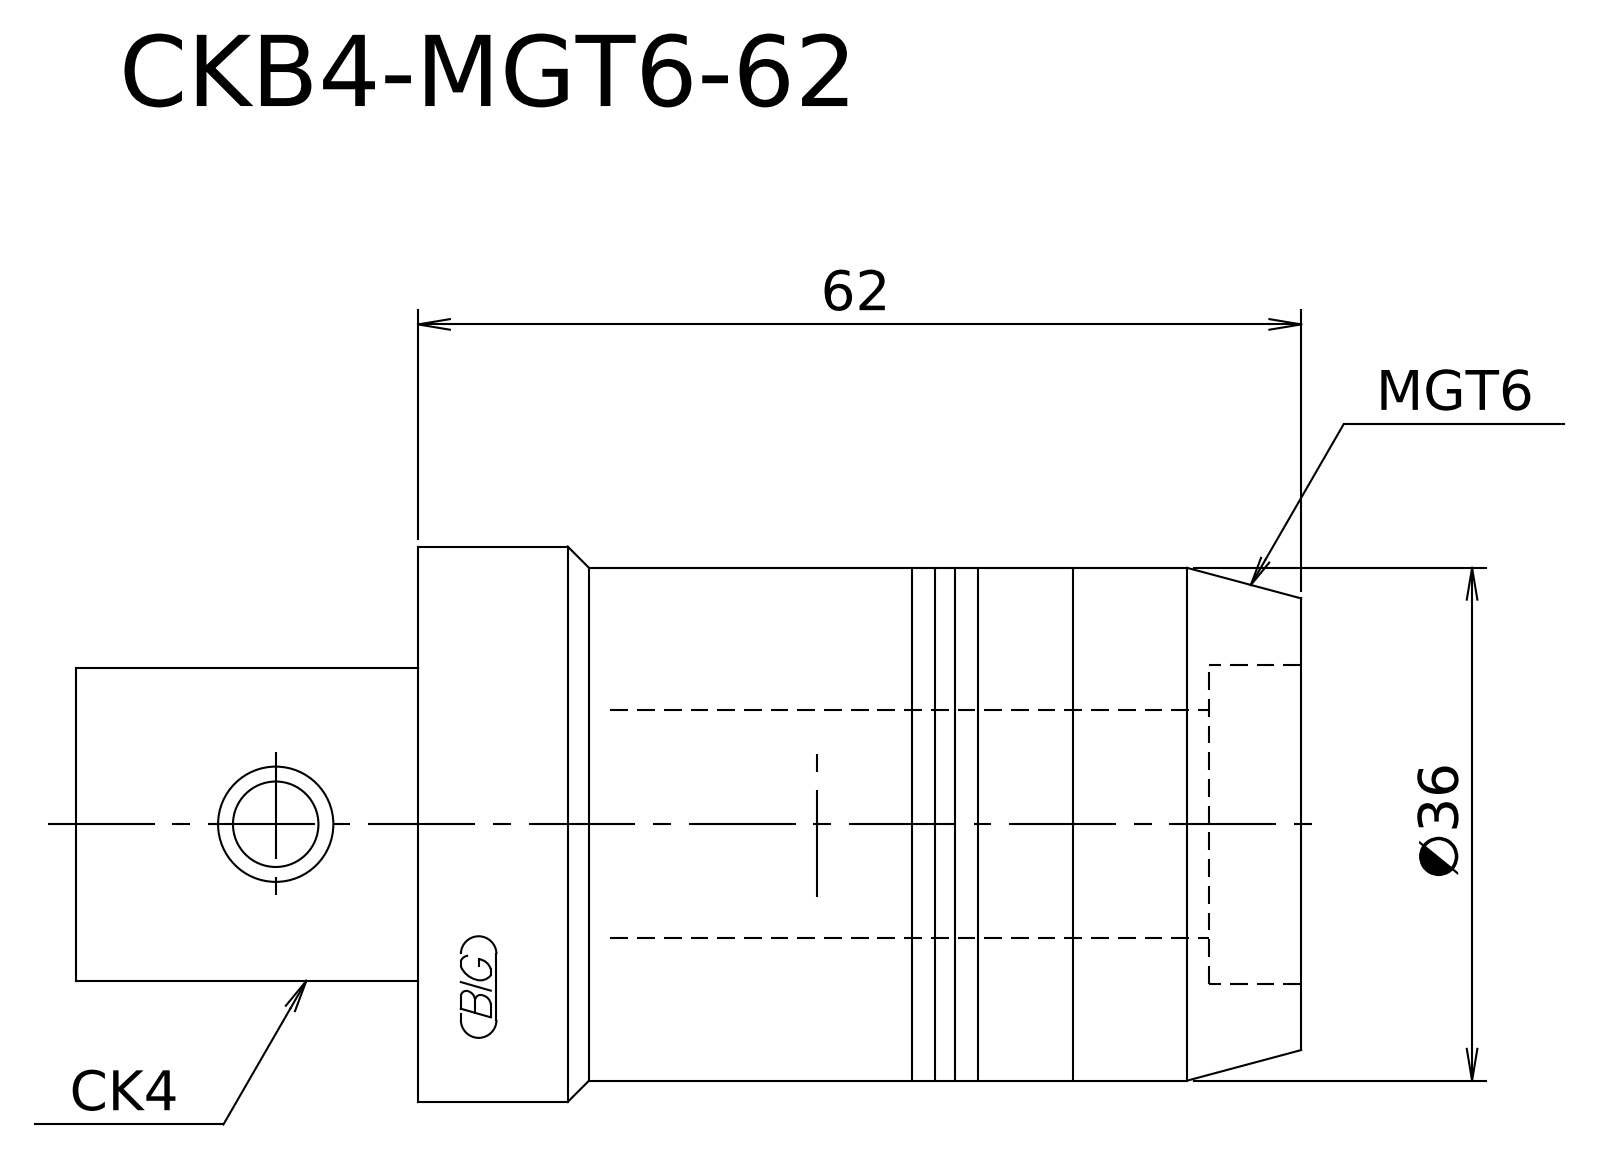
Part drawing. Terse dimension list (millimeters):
written by: Kubotek KeyCreator V8.5.1 (14335) (CONFIG_CONTROL_DESIGN)
unit: mm
bodies: 1 solid, 14 faces (2 planar, 6 cylindrical, 6 other)
size: 62 × 39 × 39
volume: 64 056 mm³; area: 9 220 mm²
bosses: 1× ⌀39, 1× ⌀36, 1× ⌀35.2
face distances: 62
